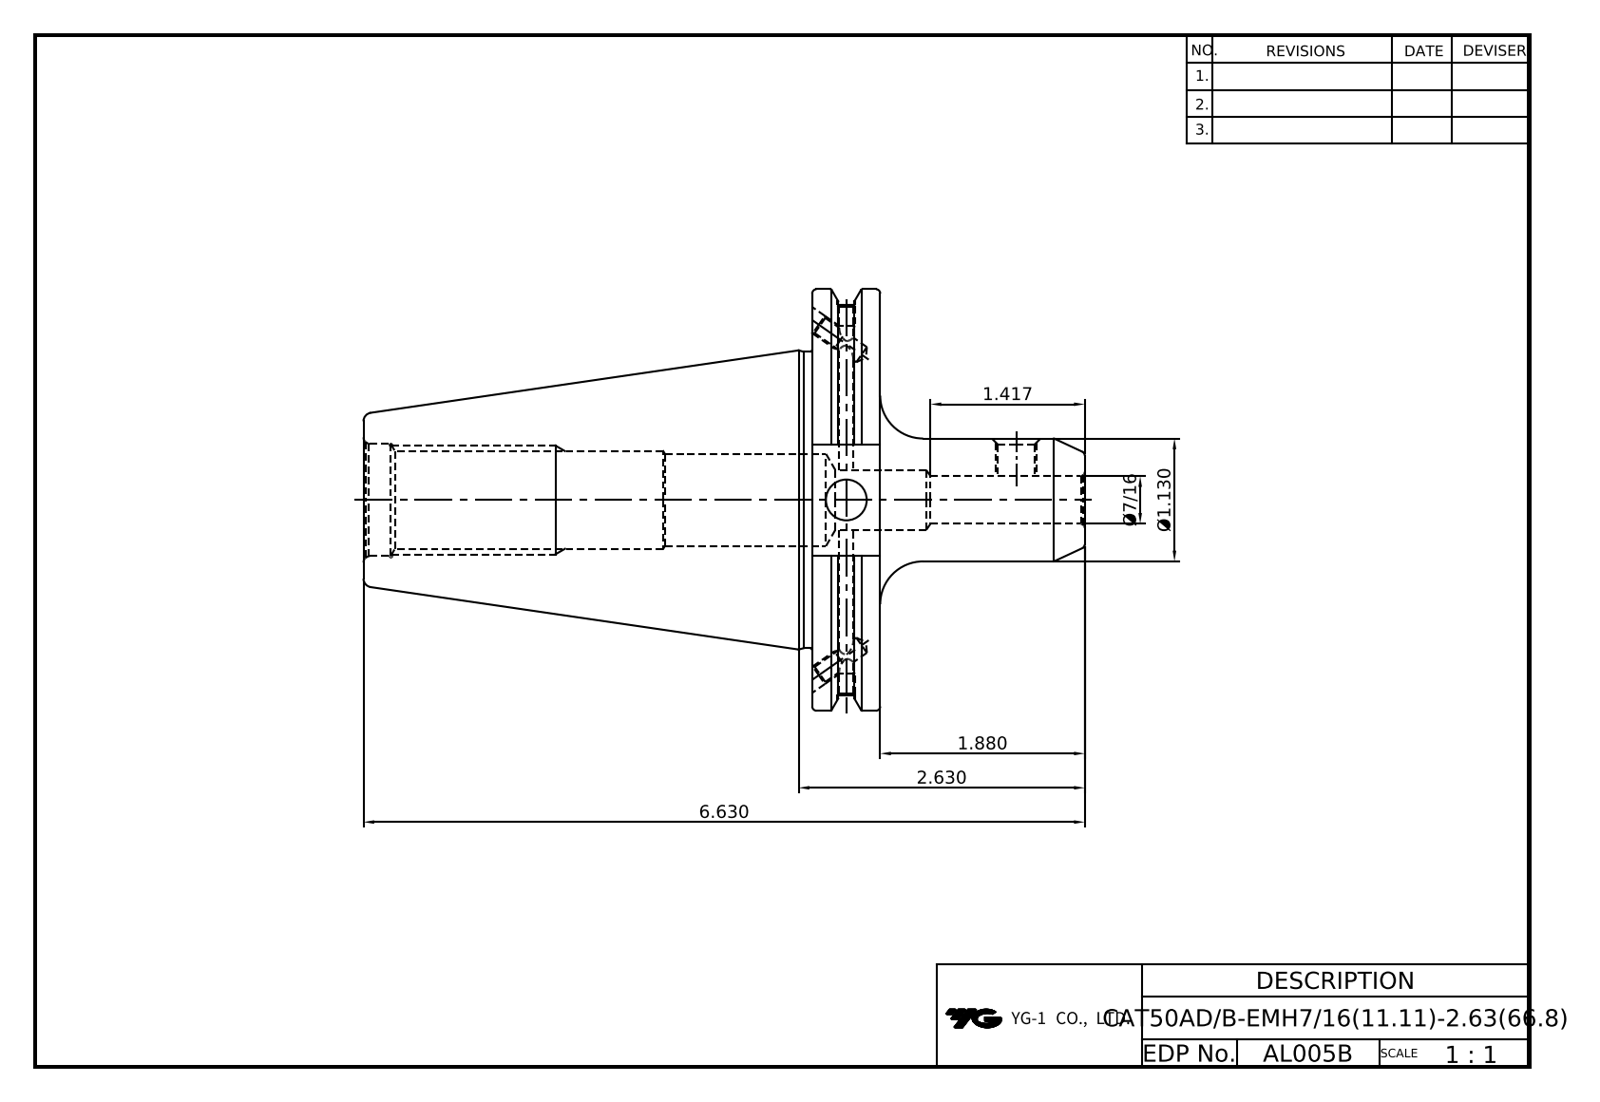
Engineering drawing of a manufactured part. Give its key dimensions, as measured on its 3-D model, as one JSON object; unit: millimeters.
{"part_name": "LO-CAT50ADB-EMH11.1125-66.8", "step_written_by": "Autodesk Inventor 2025 (AUTOMOTIVE_DESIGN)", "units": "millimeters", "bodies": {"solids": 1, "faces": 81, "planar": 35, "cylindrical": 22, "other": 24}, "overall_size": [168.4, 98.42, 94.69], "volume_mm3": 346312, "surface_area_mm2": 50232, "round_holes": [[4.13, 2], [4.2, 2], [5, 2], [8.38, 1], [9.53, 1], [11.11, 1], [14, 1], [21.97, 1], [26.2, 1]], "round_bosses_or_shafts": [[98.42, 1], [91.29, 1], [69.25, 1], [28.7, 1]], "face_to_face_distances": [15.88, 104.77, 120.65, 73.03, 25.9, 168.4, 63.63, 47.75, 110.82, 6.05]}
